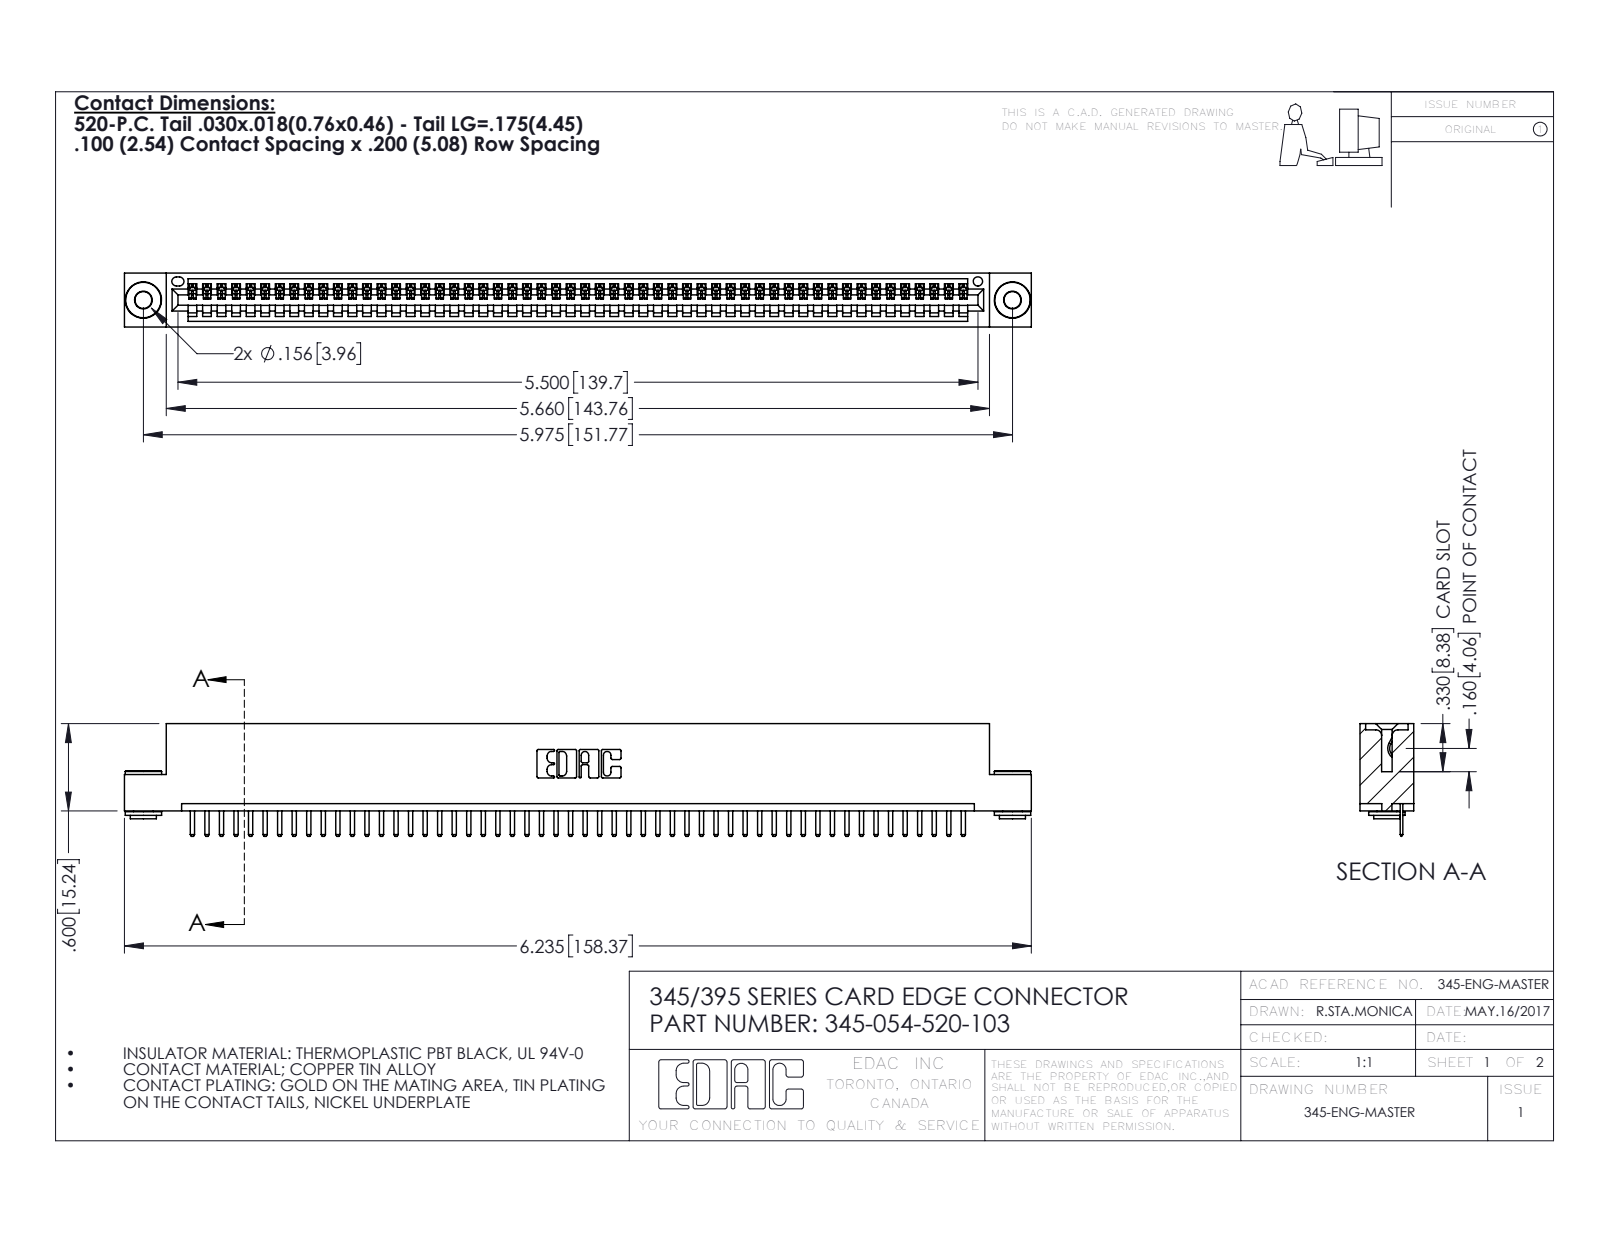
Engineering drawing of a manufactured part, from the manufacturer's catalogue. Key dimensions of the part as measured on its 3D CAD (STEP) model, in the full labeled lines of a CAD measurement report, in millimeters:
Part name (STEP PRODUCT): 345 Part_Flush Mounting Lugs - 0.156 Dia-TH; 345-054-520-103; 345-250-002_345-250-002-102; 345-292-001_345-293-120
STEP written by: SolidWorks 2016 (CONFIG_CONTROL_DESIGN)
Units: millimetres
Bodies: 57 solids, 3512 faces (2358 planar, 1146 cylindrical, 8 other)
Overall size (bounding box): 158.4 × 19.7 × 9.4
Volume: 15 000 mm³ · Surface area: 19 810 mm²
Round holes (diameter × count): ⌀2.9 ×2, ⌀4 ×2, ⌀1.6 ×1
Round bosses / shafts (diameter × count): ⌀6.4 ×2, ⌀4.6 ×2, ⌀3.5 ×2
Partial cylindrical surfaces — rounded edges, fillets, slot ends (radius × count): R0.3 ×110, R0.2 ×108, R0.3 ×22, R0.2 ×6, R0.8 ×6, R0.7 ×3, R0.8 ×2, R1 ×2
Main face-to-face distances: 1.8, 7.6, 9.4, 5.1, 0.6, 2.5, 6.9, 5.7, 1.8, 3.8
Hole centre spacings: 6.9, 145.8, 151.8
